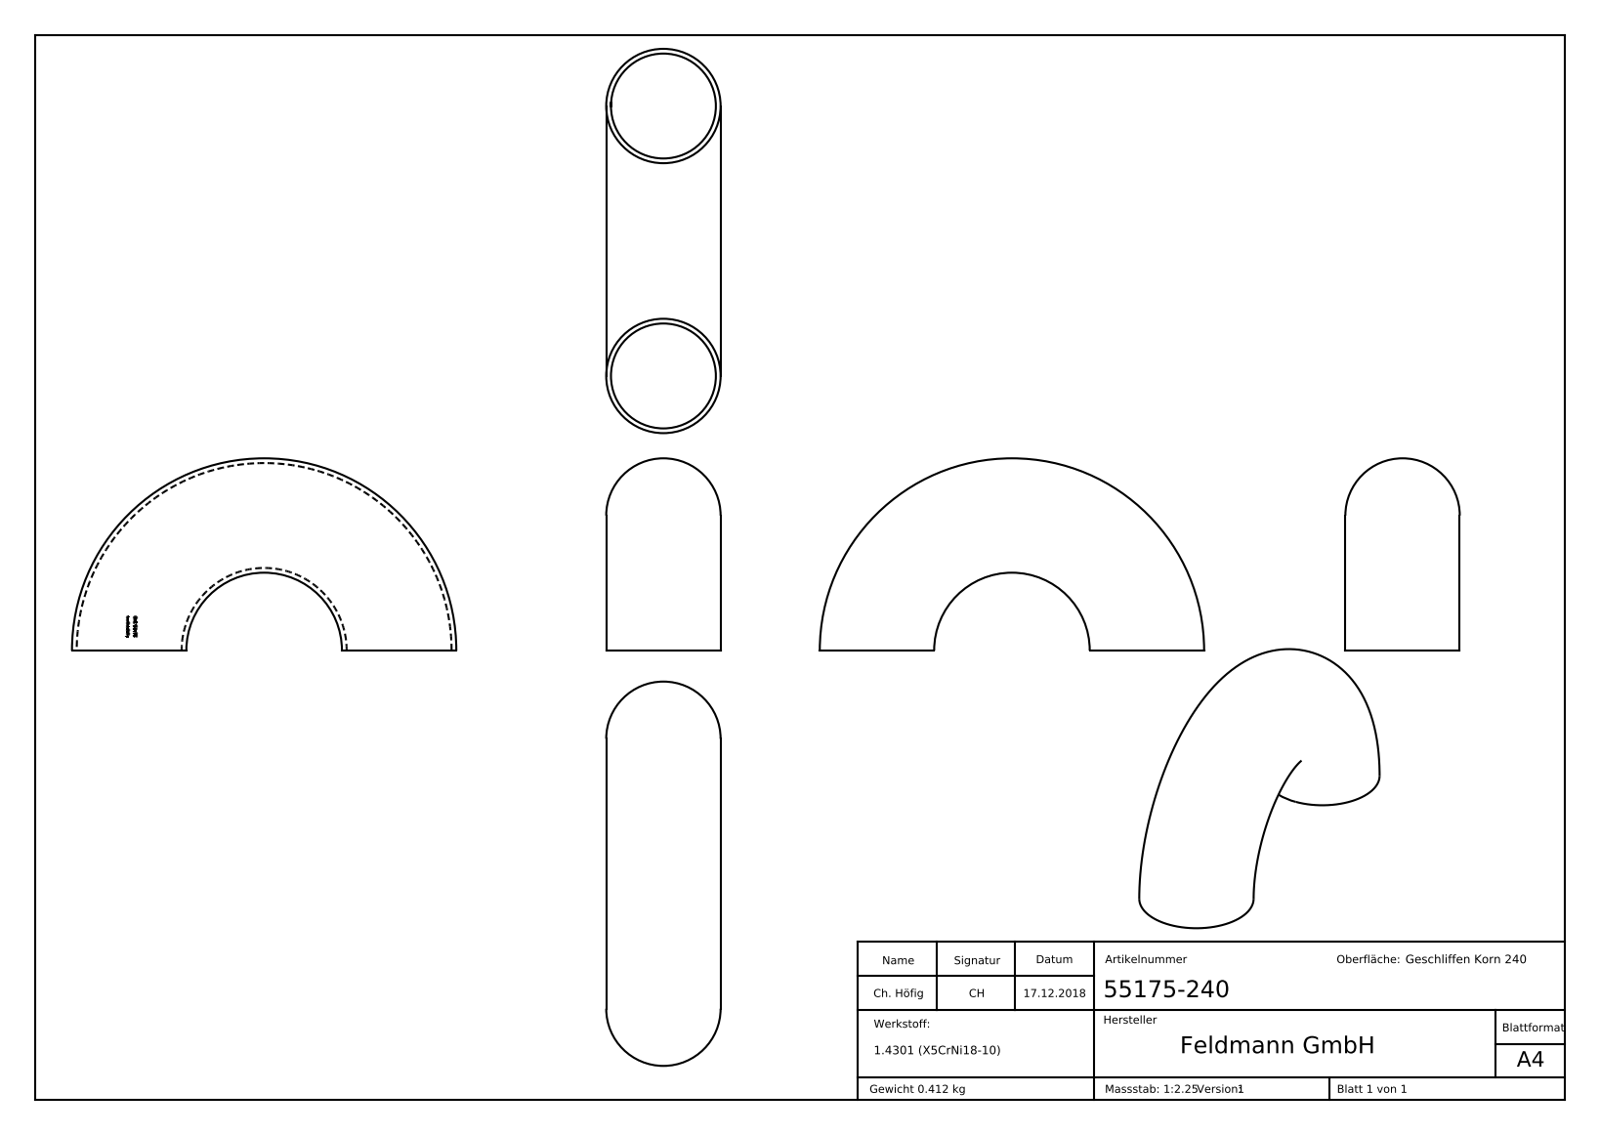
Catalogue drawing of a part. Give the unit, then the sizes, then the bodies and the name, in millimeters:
Units: millimetres
Overall size (bounding box): 162.3 × 81.15 × 48.3
Main face-to-face distances: 0.39, 1.26, 2.97, 4.23, 3.39, 3.27, 0.45, 1.19, 2.4, 0.99
Volume: 52 093 mm³ · Surface area: 52 685 mm²
Bodies: 1 solid, 222 faces (109 planar, 0 cylindrical, 113 other)
Part name (STEP PRODUCT): 55175-240
STEP written by: SolidWorks 2015 (CONFIG_CONTROL_DESIGN)
